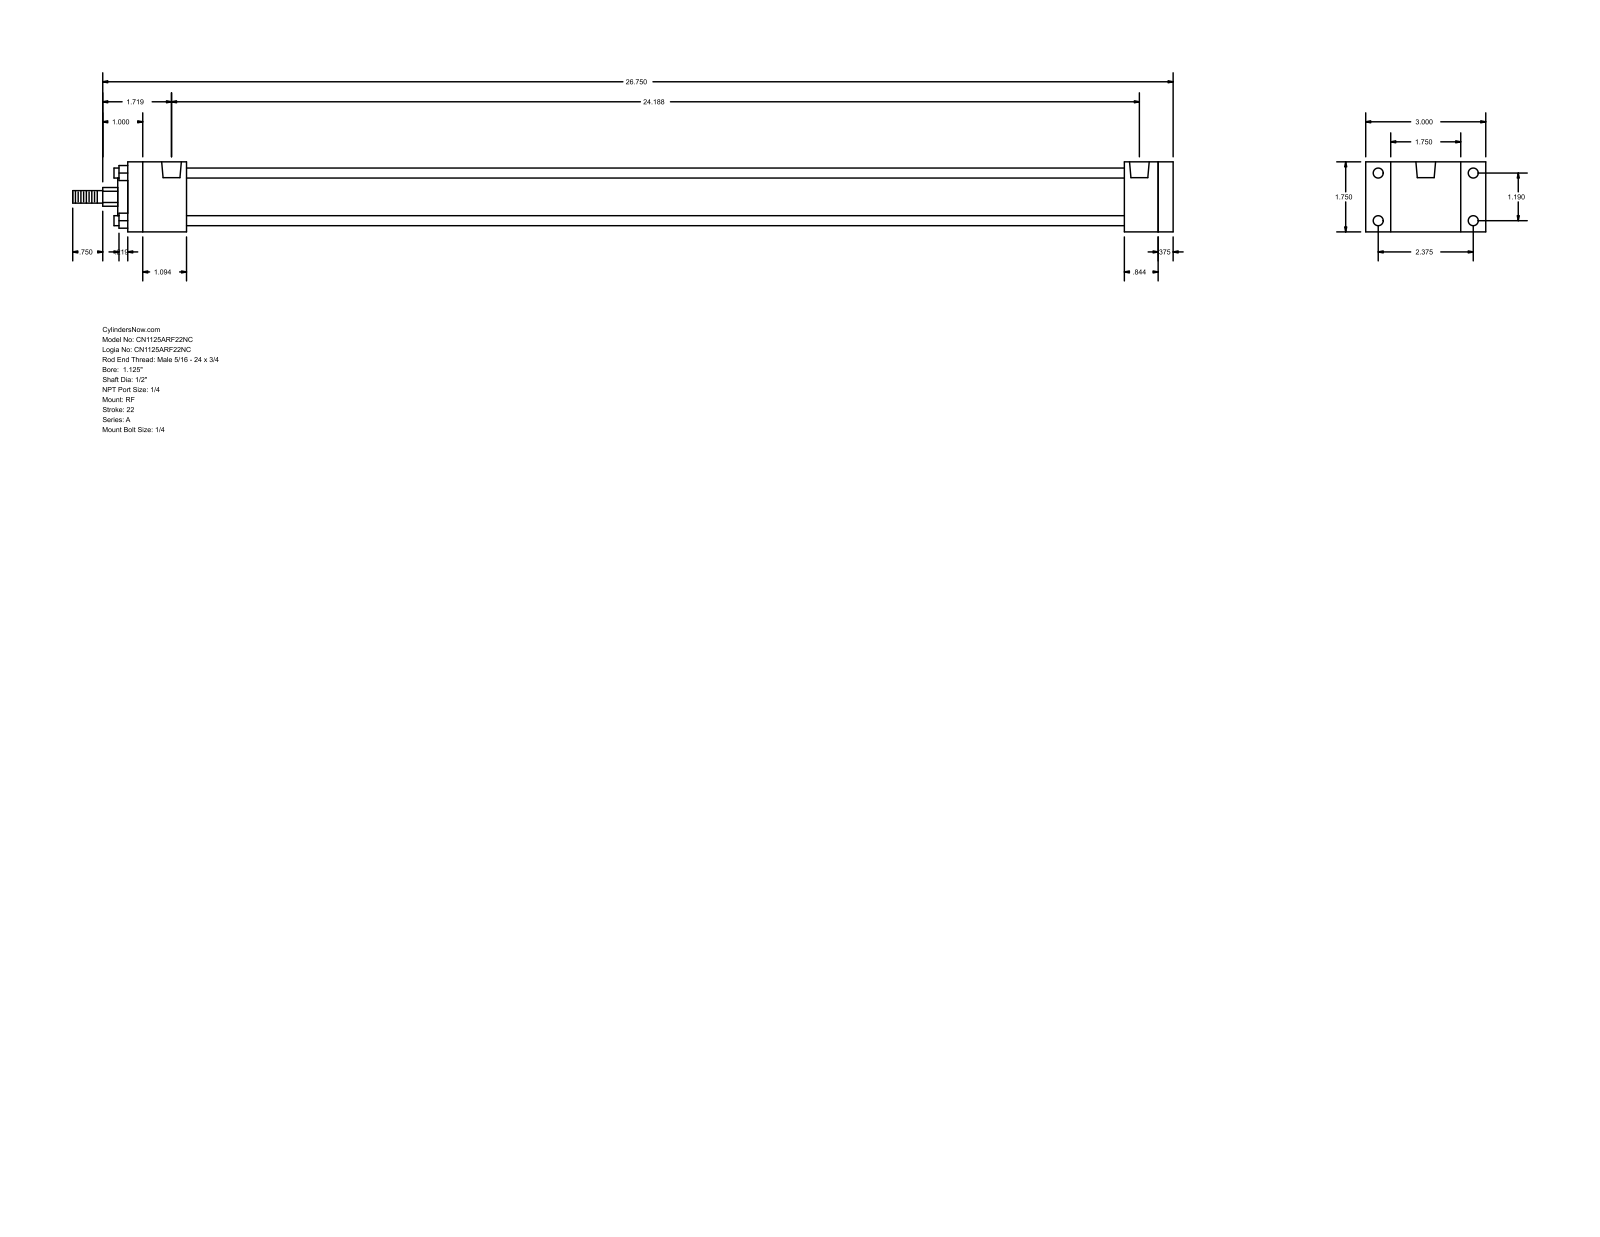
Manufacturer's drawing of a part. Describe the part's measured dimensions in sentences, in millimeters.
The part is named "A_RF__0112_0.5". Its 3-D file was written by "GSSL Pune (CONFIG_CONTROL_DESIGN)". It is 0 solids with 92 faces: 64 planar, 28 cylindrical and 0 other. Overall it measures 698.5 by 76.2 by 44.45 millimeters. Round holes: 4 of diameter 5.56, 4 of diameter 6.35, 2 of diameter 12.49. Round bosses or shafts: 4 of diameter 6.35, 1 of diameter 31.88, 1 of diameter 23.81, 1 of diameter 12.7, 1 of diameter 7.94. Partial cylindrical surfaces (rounded edges, fillets, slot ends): 1 of radius 5.94. The main face-to-face distances are 44.46, 9.53, 663.57, 654.04, 37.3, 632.61, 595.31, 616.74, 626.27, 21.43. The hole center spacings are 30.22, 60.32, 67.47, 611.19, 1.58, 1.59, 612.77, 612.78.
